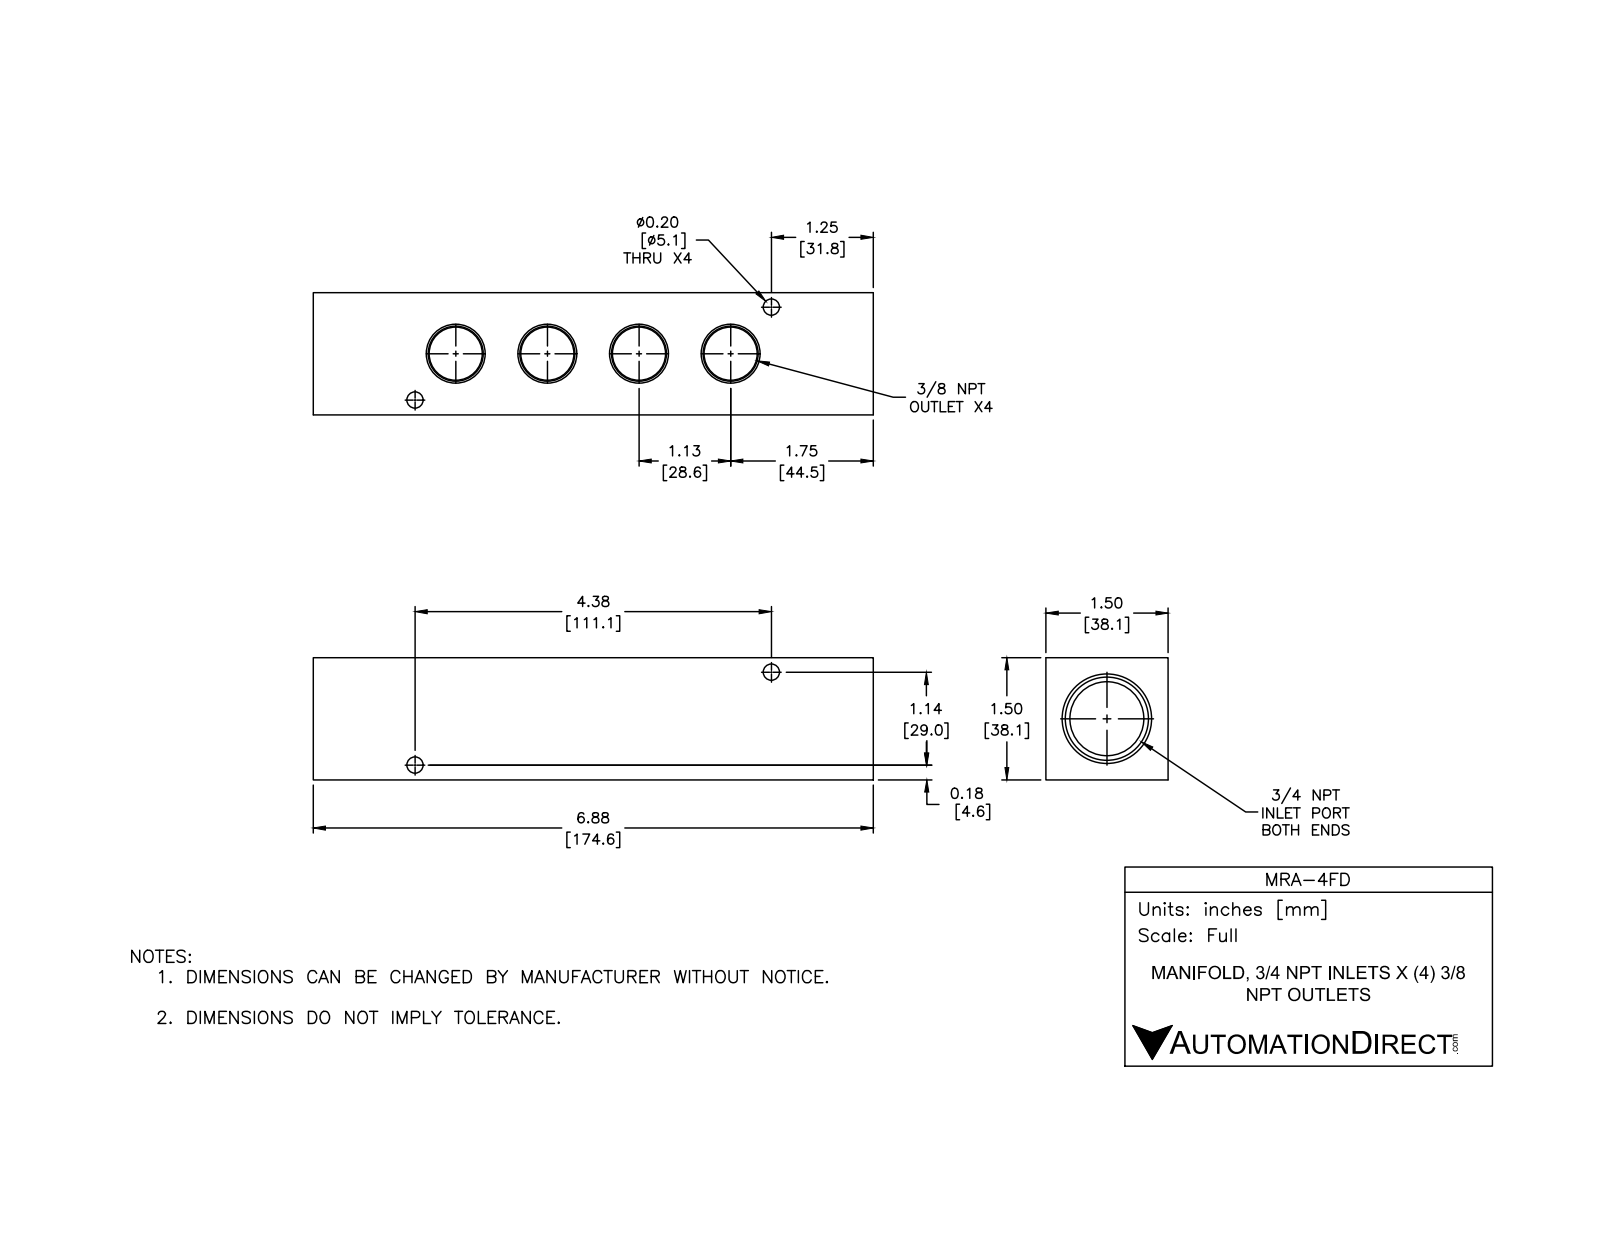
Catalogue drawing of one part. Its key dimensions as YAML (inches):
part_name: "MRA-4FD"
step_written_by: "SolidWorks 2015 (CONFIG_CONTROL_DESIGN)"
units: inches
bodies: {solids: 1, faces: 58, planar: 16, cylindrical: 18, other: 24}
overall_size: [6.875, 1.5, 1.5]
volume: 10.18
surface_area: 67.56
round_holes:
  - {diameter: 0.2, count: 4}
  - {diameter: 0.906, count: 1}
face_to_face_distances: [1.5, 6.875, 0.55, 6.325, 5.775, 1.09, 0.41]
hole_center_spacings: [4.521]
